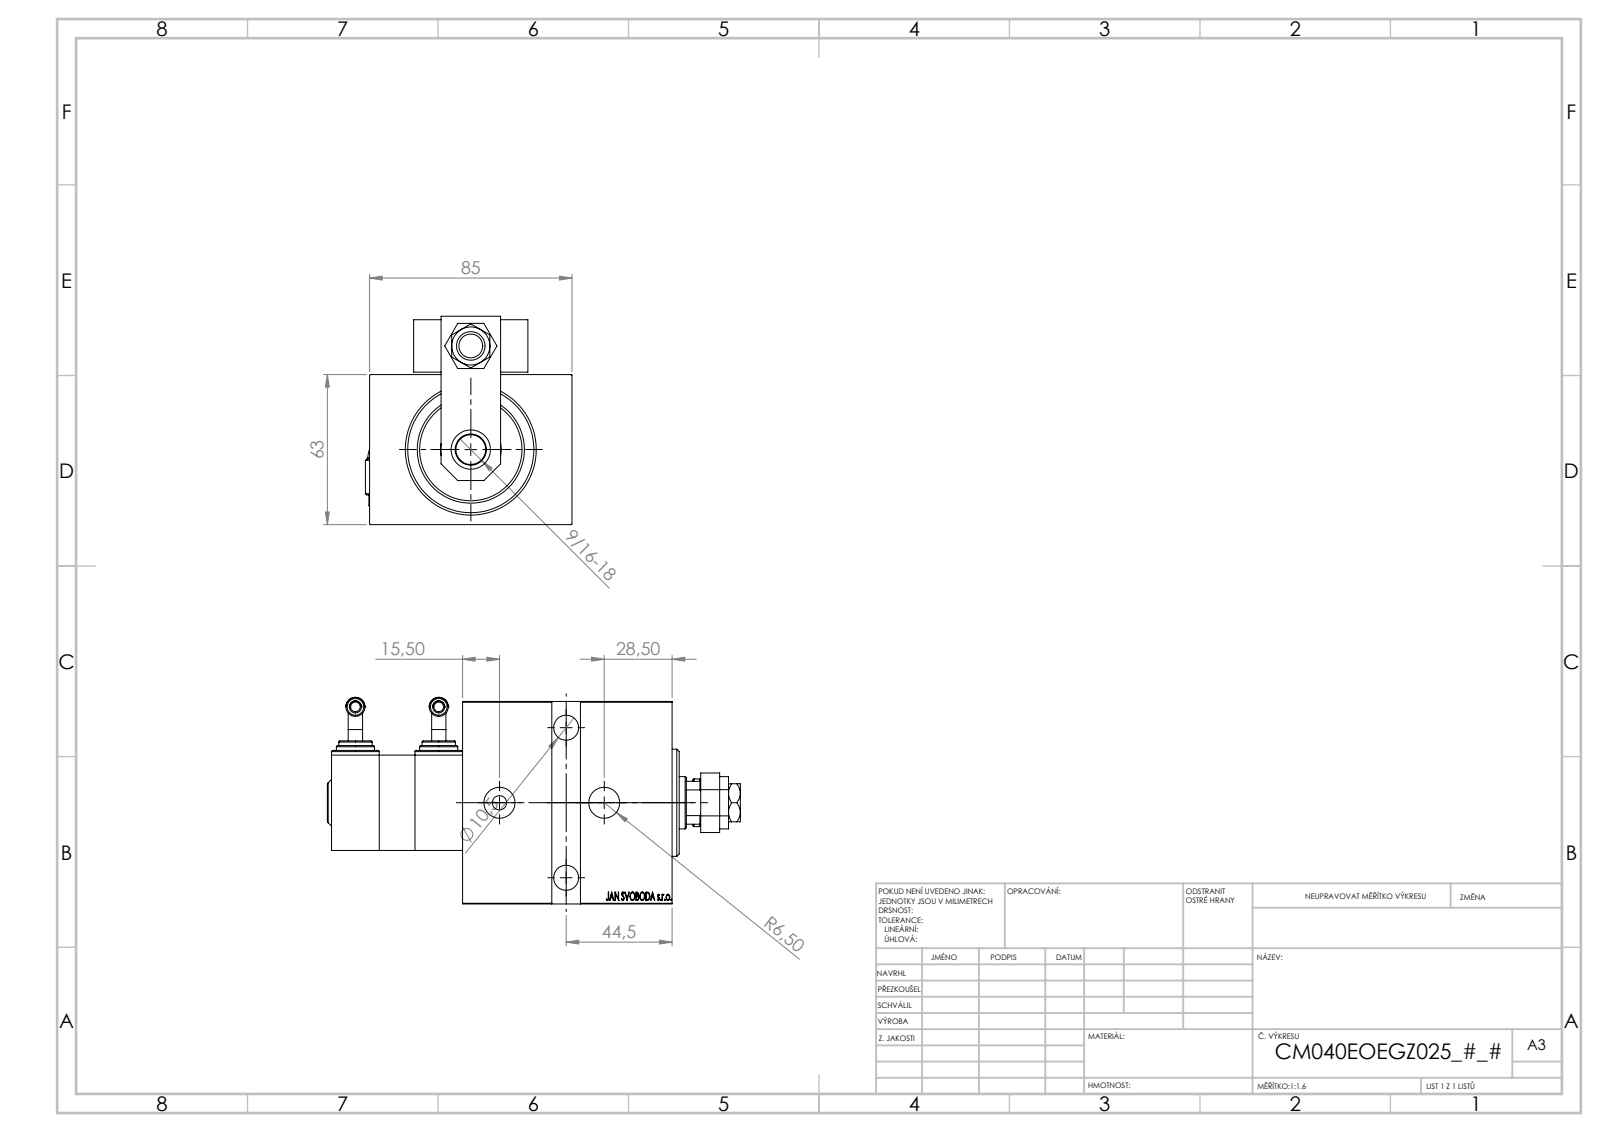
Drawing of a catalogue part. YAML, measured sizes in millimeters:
part_name: "TYC_P; V450CM_VC_B; SWITCH DIM W_B; SWITCH P (+7 more)"
step_written_by: "SolidWorks 2019 (CONFIG_CONTROL_DESIGN)"
units: millimeters
bodies: {solids: 14, faces: 1092, planar: 523, cylindrical: 104, other: 465}
overall_size: [173.5, 87.5, 86.76]
volume: 600793
surface_area: 118220
round_holes:
  - {diameter: 4, count: 4}
  - {diameter: 8, count: 4}
  - {diameter: 13, count: 3}
  - {diameter: 16.5, count: 3}
  - {diameter: 10.5, count: 2}
  - {diameter: 12, count: 1}
  - {diameter: 12.5, count: 1}
  - {diameter: 14, count: 1}
  - {diameter: 22, count: 1}
  - {diameter: 25.5, count: 1}
  - {diameter: 40, count: 1}
  - {diameter: 53, count: 1}
round_bosses_or_shafts:
  - {diameter: 20, count: 3}
  - {diameter: 6, count: 3}
  - {diameter: 16, count: 2}
  - {diameter: 14, count: 2}
  - {diameter: 8, count: 2}
  - {diameter: 5.04, count: 2}
  - {diameter: 45, count: 1}
  - {diameter: 42, count: 1}
partial_cylinders:
  - {radius: 3, count: 1}
  - {radius: 10.5, count: 1}
face_to_face_distances: [85, 35, 63, 20, 88, 108, 15, 12, 22.5, 32]
hole_center_spacings: [12.81, 20, 23.26, 35.33, 41.93, 42.15, 42.79, 52.95]
